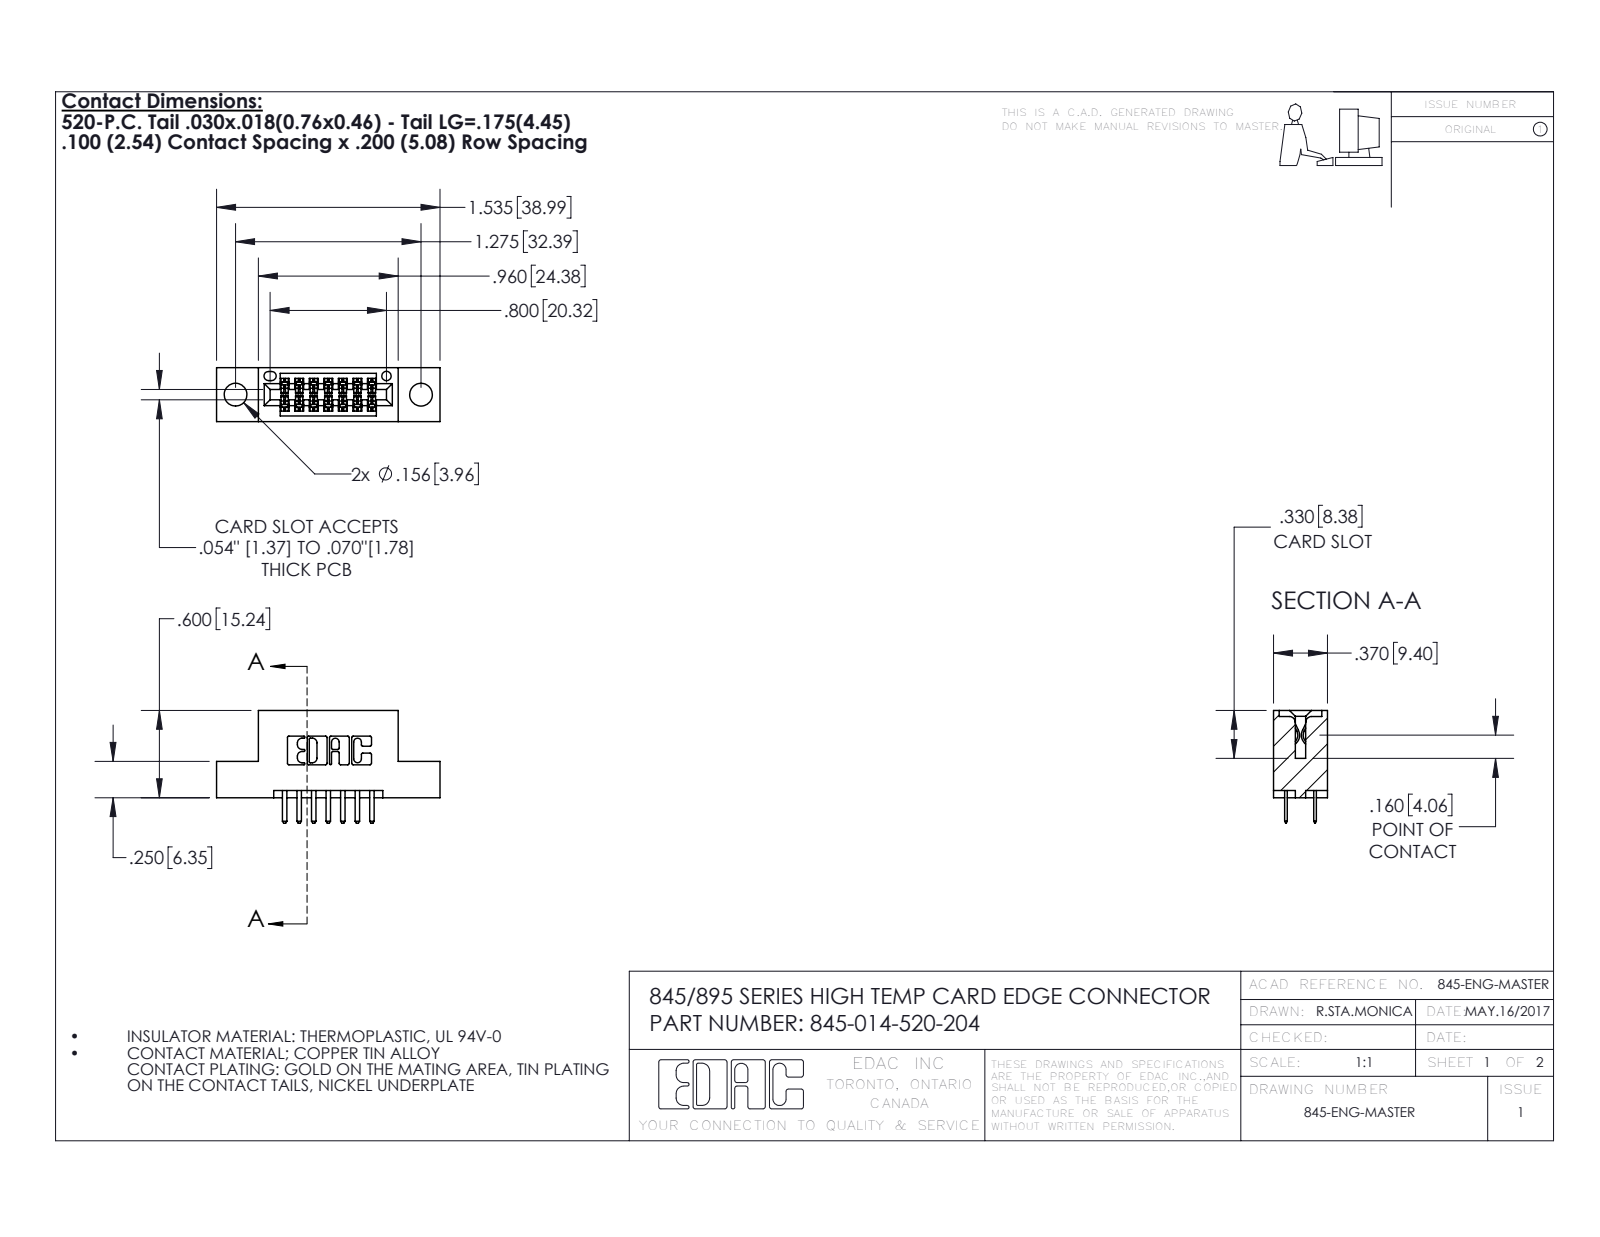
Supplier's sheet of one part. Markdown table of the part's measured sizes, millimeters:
| quantity | value |
| --- | --- |
| part name | 345-292-001_345-293-120; 345-014-520-204; 345 Part_Flush Mounting Lugs - 0.156 Dia-TH |
| STEP written by | SolidWorks 2016 (CONFIG_CONTROL_DESIGN) |
| units | millimeters |
| bodies | 15 solids, 882 faces (570 planar, 312 cylindrical, 0 other) |
| overall size | 39 × 19.7 × 9.4 |
| volume | 3 380 mm³ |
| surface area | 4 103 mm² |
| round holes (diameter × count) | 4 × 2, 1.6 × 1 |
| partial cylindrical surfaces (radius × count) | 0.3 × 22, 0.2 × 21, 0.3 × 18, 0.2 × 6, 0.8 × 6, 0.7 × 3, 0.4 × 2, 0.5 × 2 |
| main face-to-face distances | 5.1, 9.4, 7.6, 1.8, 2.5, 7.6, 2.5, 6.9, 0.6, 1.5 |
| hole center spacings | 6.9, 26.5, 32.4 |
